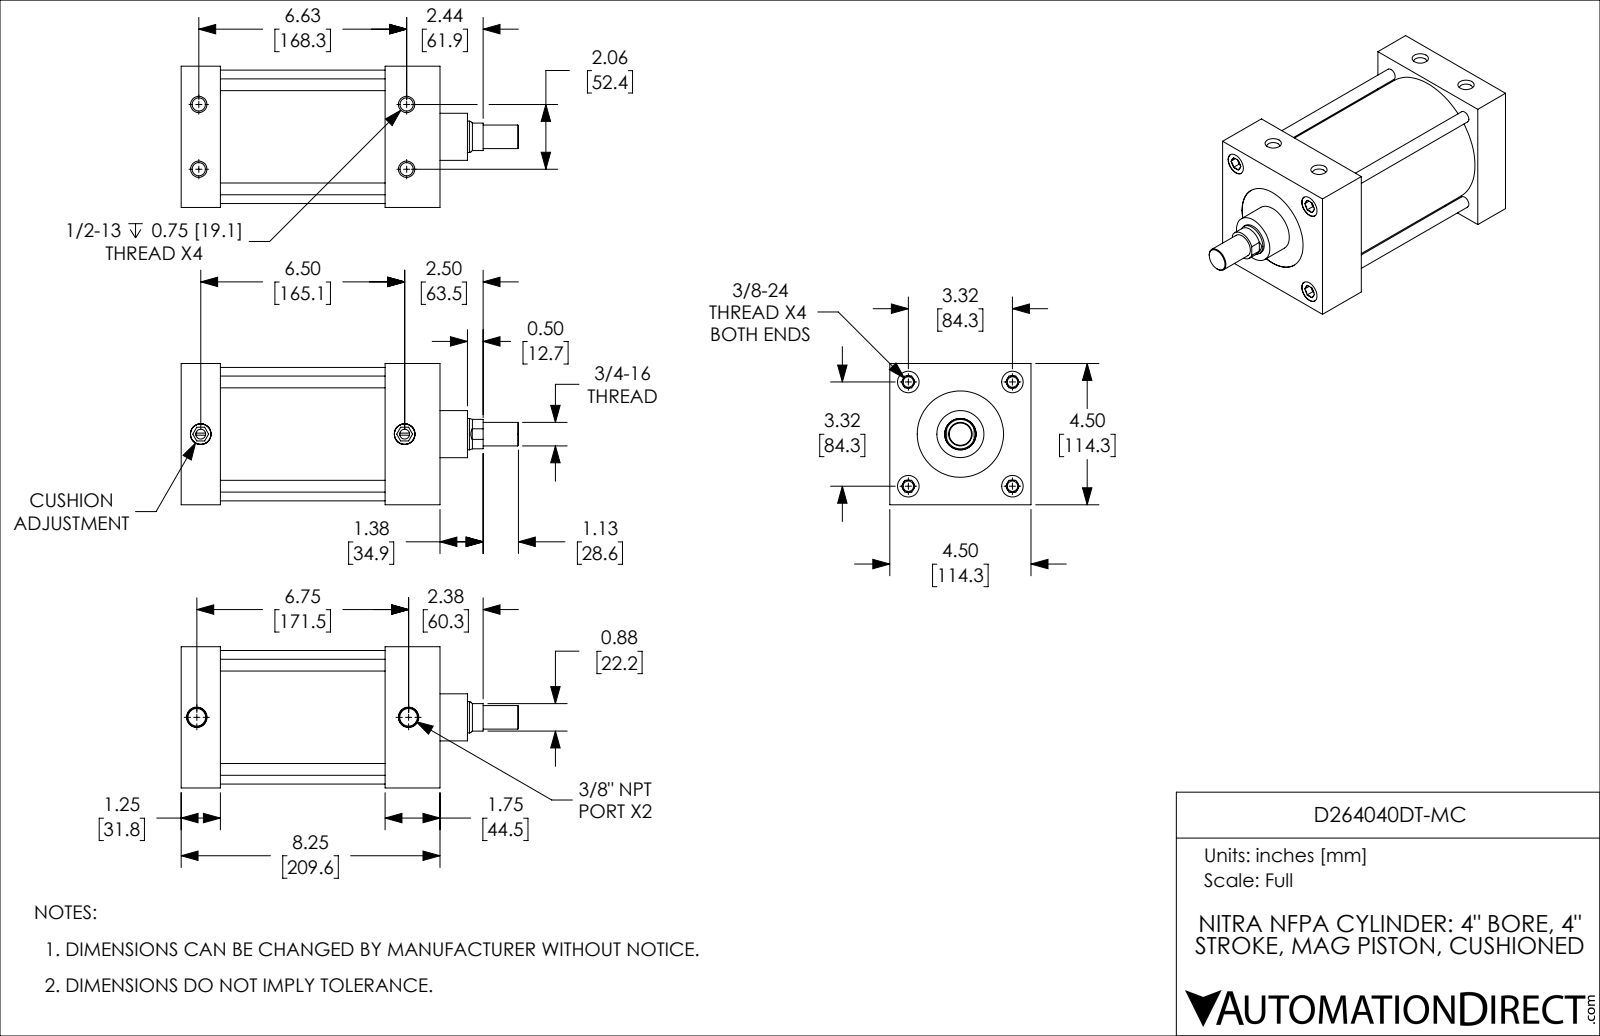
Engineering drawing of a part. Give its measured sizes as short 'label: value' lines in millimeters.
name: D264040DT-MC_BODY; D264040DT-MC_PISTON_KK1; D264040DT-MC_CUSHION; D264040DT-MC
written by: SolidWorks 2019 (CONFIG_CONTROL_DESIGN)
unit: mm
bodies: 4 solids, 246 faces (90 planar, 78 cylindrical, 78 other)
size: 273.1 × 114.3 × 114.3
volume: 1 481 000 mm³; area: 252 800 mm²
holes: 4× ⌀8.4, 4× ⌀10.7, 4× ⌀17.4, 2× ⌀7.9, 2× ⌀14.3, 2× ⌀16.7, 1× ⌀25.4, 1× ⌀69.9, 1× ⌀101.6
bosses: 4× ⌀9.5, 2× ⌀16.7, 1× ⌀108, 1× ⌀101.6, 1× ⌀38.1, 1× ⌀25.4, 1× ⌀19.1
rounds: 1× R11.9
face distances: 31.8, 114.3, 165.1, 133.4, 209.6, 177.8, 44.5, 63.5, 101.6, 146.1
hole spacings: 26.2, 59.6, 84.3, 171.9, 52.4, 119.3, 168.3, 176.2
